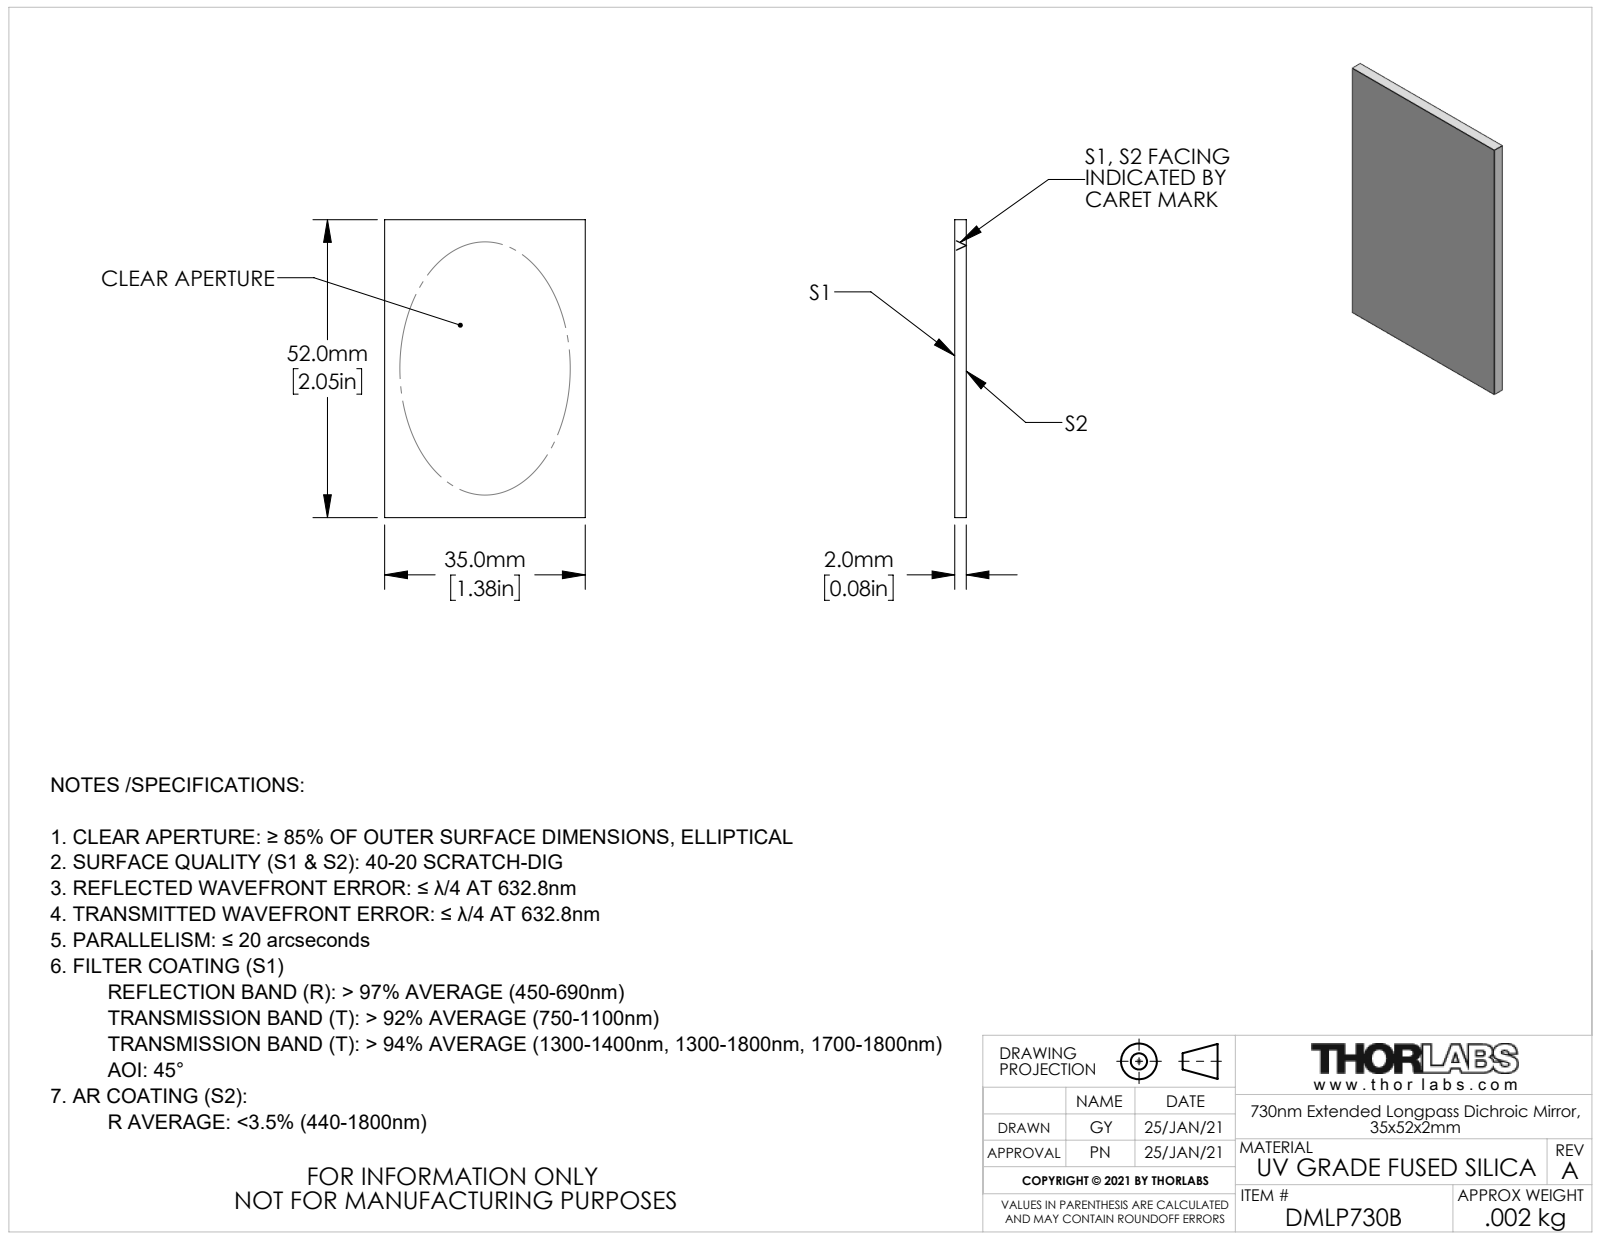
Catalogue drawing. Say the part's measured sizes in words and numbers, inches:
The part is named "TTN223100-E0W". Its 3-D file was written by "SolidWorks 2018 (AUTOMOTIVE_DESIGN)". It is 0 solids with 6 faces: 6 planar, 0 cylindrical and 0 other. Overall it measures 2.047 by 1.378 by 0.079 inches. The main face-to-face distances are 0.079, 1.378, 2.047.
